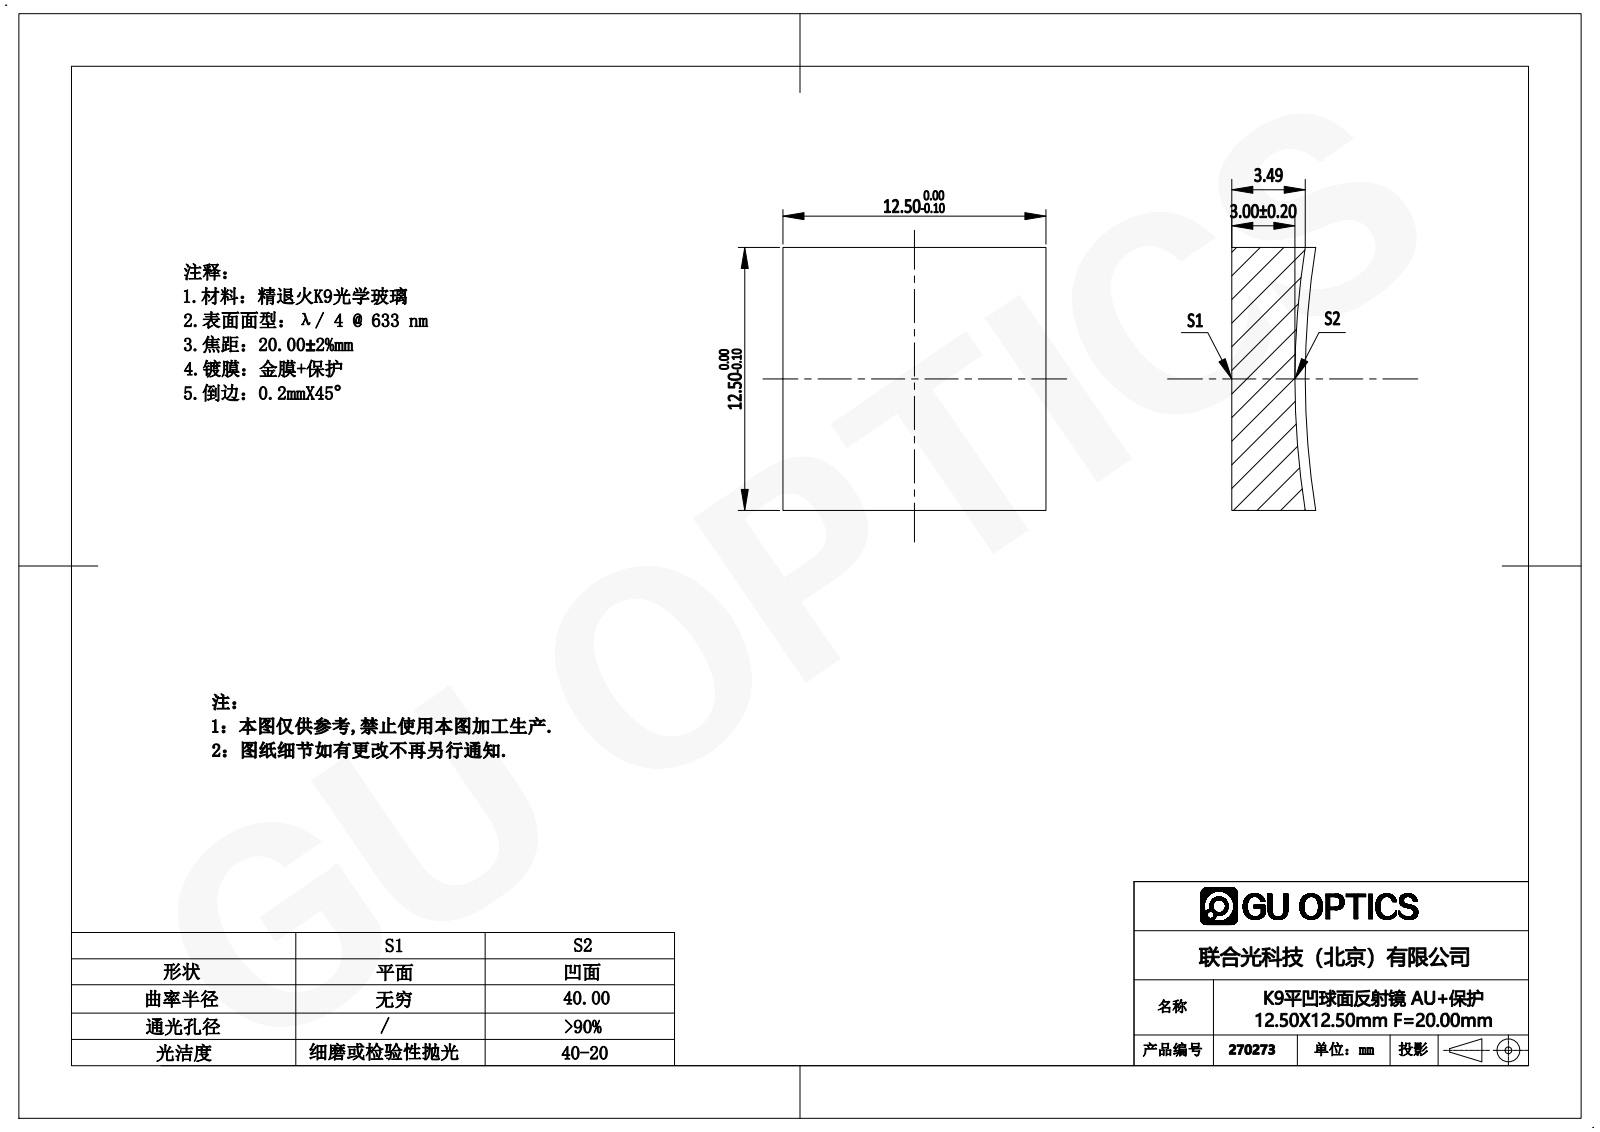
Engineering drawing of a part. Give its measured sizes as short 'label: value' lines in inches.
name: 270013
written by: SolidWorks 2019 (AUTOMOTIVE_DESIGN)
unit: in
bodies: 1 solid, 7 faces (5 planar, 0 cylindrical, 2 other)
size: 0.492 × 0.492 × 0.157
volume: 0.032 in³; area: 0.77 in²
face distances: 0.492
